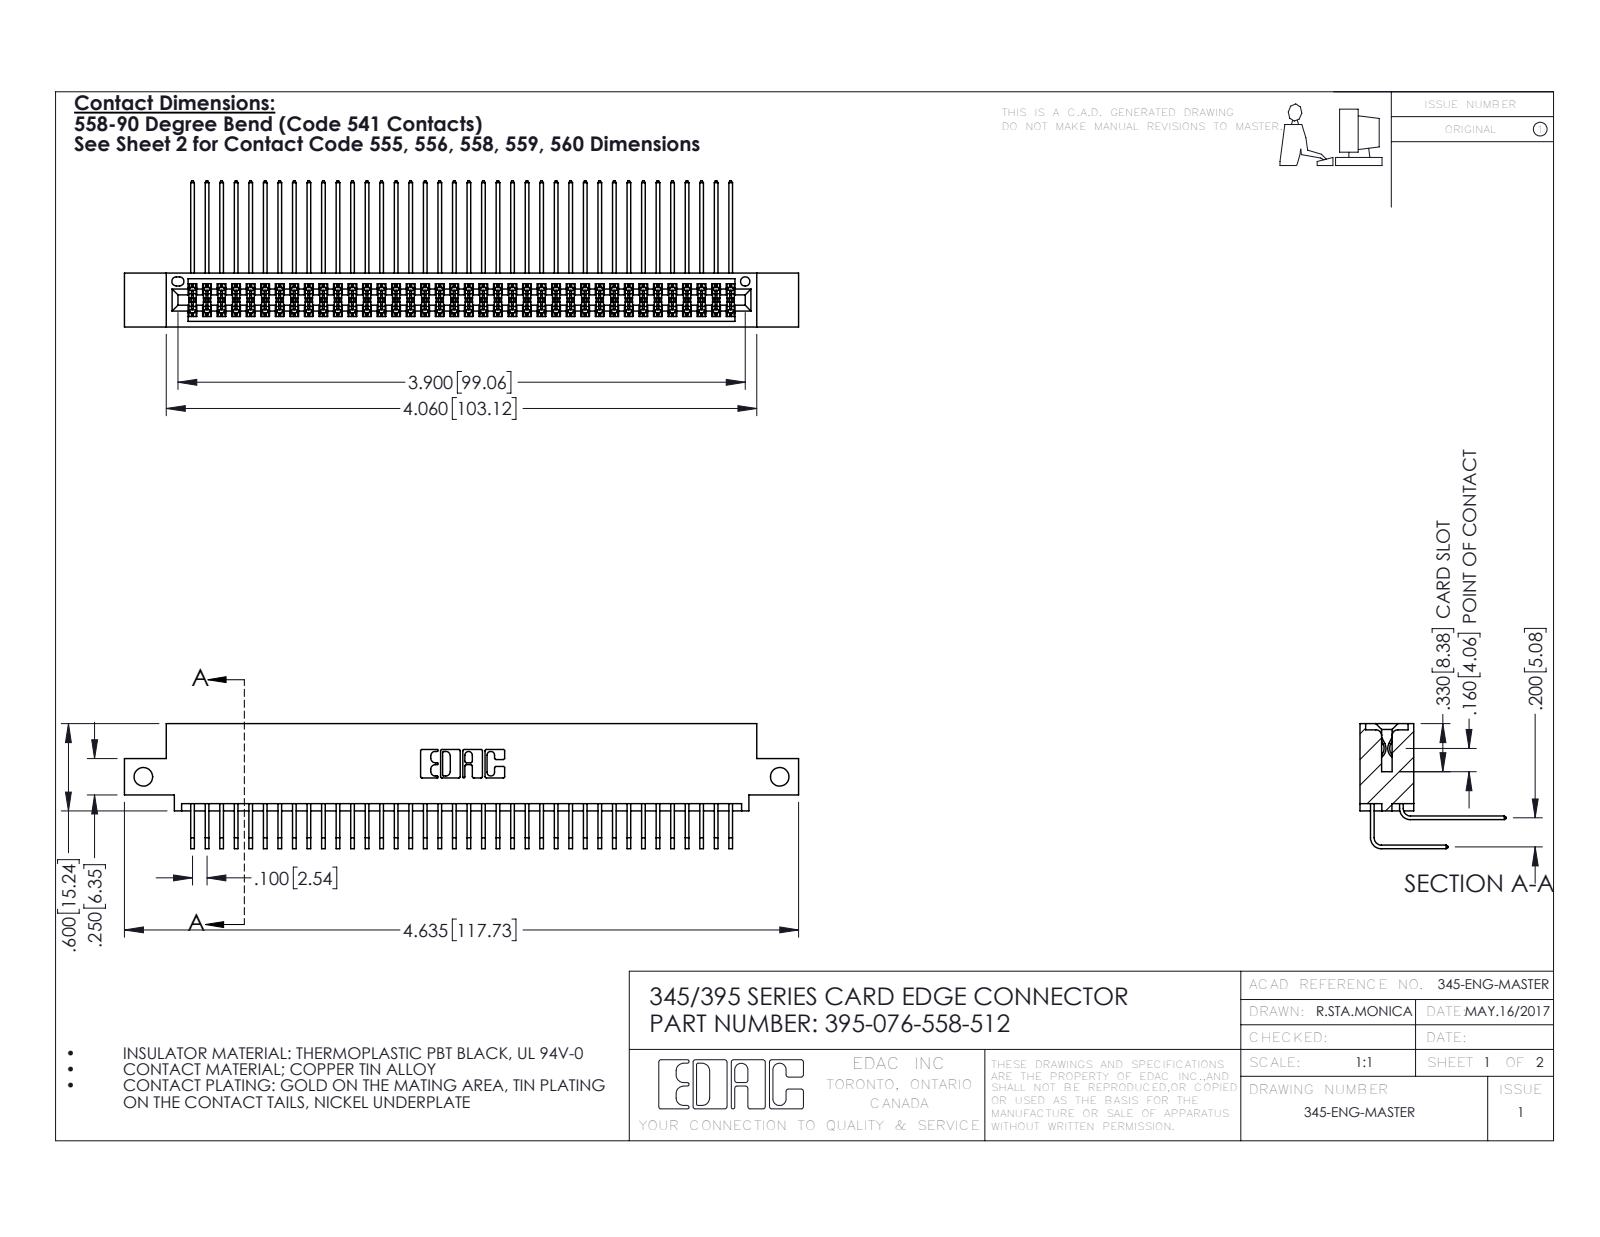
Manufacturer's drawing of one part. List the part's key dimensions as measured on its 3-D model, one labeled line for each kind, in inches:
Part name (STEP PRODUCT): 395-076-558-512; 345 Part_0.110 Offset - Side Mount; 345-292-001_558 559 Tail - 1; 345-292-001_558 Tail - 2
STEP written by: SolidWorks 2016 (CONFIG_CONTROL_DESIGN)
Units: inches
Bodies: 77 solids, 4082 faces (2744 planar, 1338 cylindrical, 0 other)
Overall size (bounding box): 4.635 × 1.005 × 0.859
Volume: 0.713 in³ · Surface area: 29.76 in²
Round holes (diameter × count): ⌀0.128 ×2, ⌀0.064 ×1
Partial cylindrical surfaces — rounded edges, fillets, slot ends (radius × count): R0.006 ×114, R0.01 ×22, R0.007 ×6, R0.031 ×6, R0.026 ×3, R0.014 ×2, R0.019 ×2, R0.022 ×2
Main face-to-face distances: 0.072, 0.298, 0.2, 0.37, 0.098, 0.272, 0.025, 0.225, 0.025, 0.175
Hole centre spacings: 4.375
